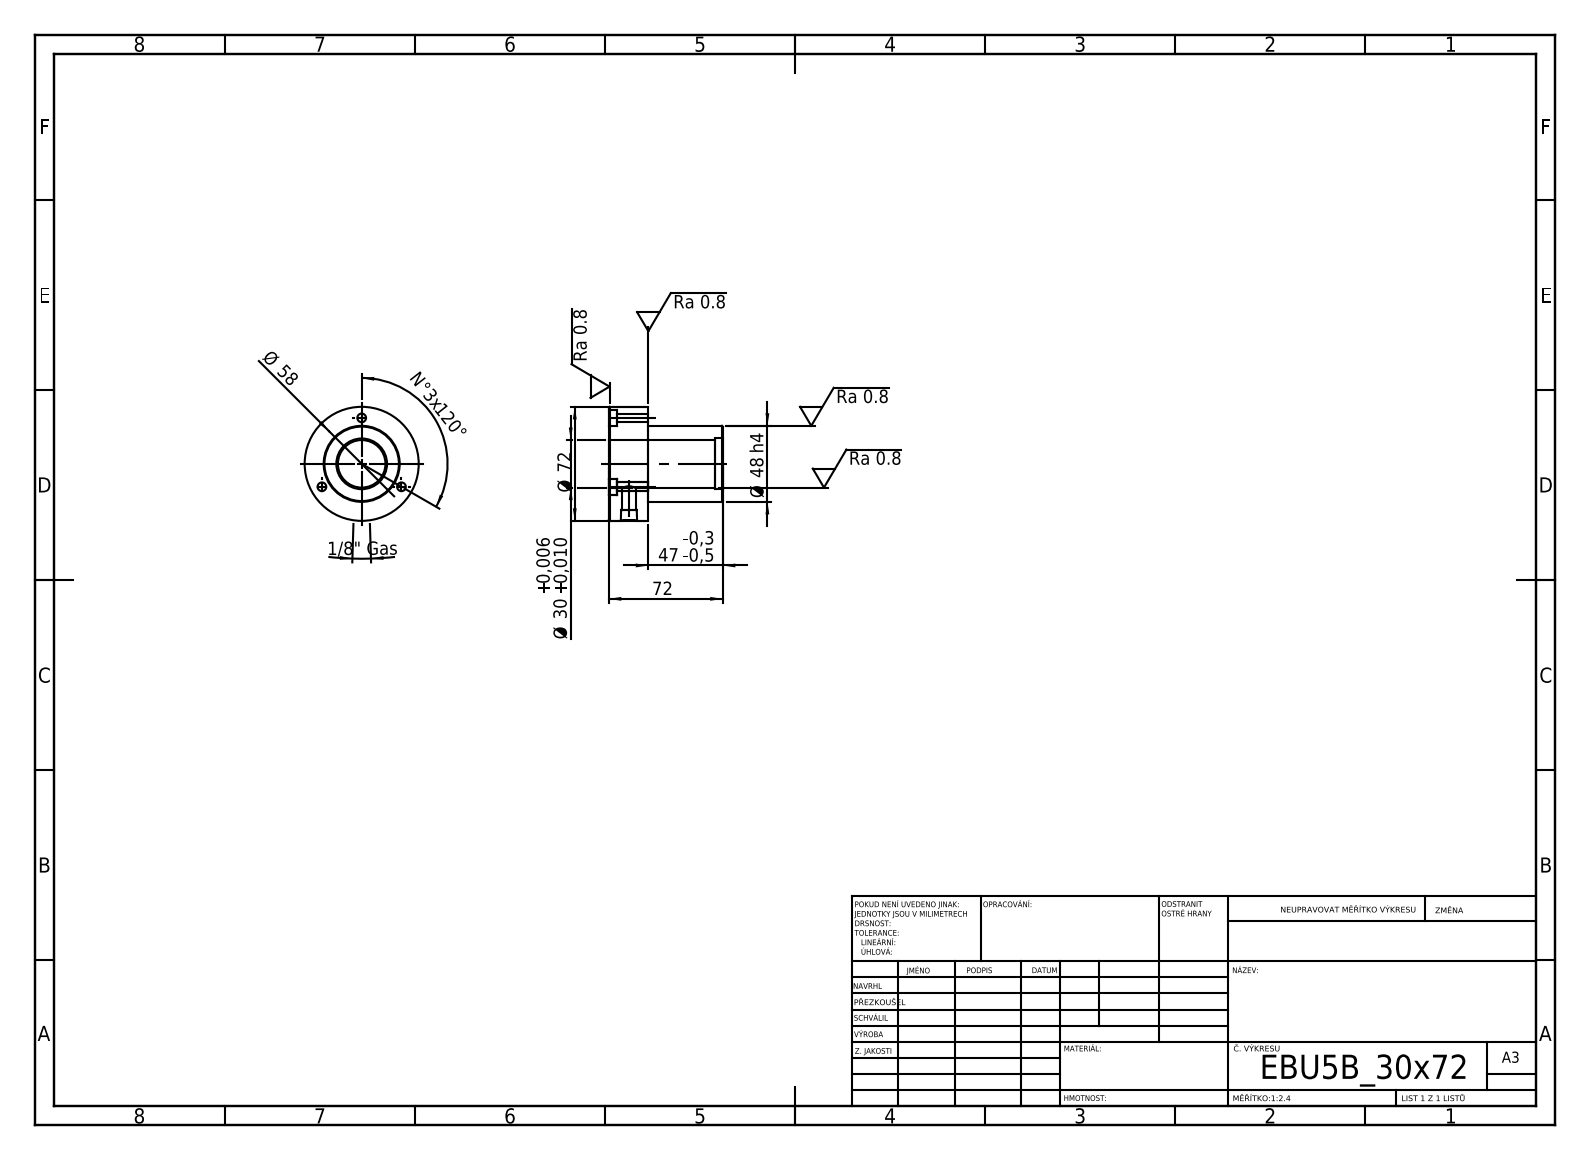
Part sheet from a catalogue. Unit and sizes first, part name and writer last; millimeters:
Units: millimetres
Overall size (bounding box): 72 × 72 × 72
Round holes (diameter × count): ⌀5.5 ×3, ⌀10 ×3, ⌀8.43 ×1, ⌀30 ×1, ⌀32 ×1
Round bosses / shafts (diameter × count): ⌀72 ×1, ⌀48 ×1
Main face-to-face distances: 25, 47, 72, 66.6, 19.6, 5.4, 5, 42, 61.6, 67
Hole centre spacings: 29, 50.23, 50.22
Volume: 131 400 mm³ · Surface area: 28 036 mm²
Bodies: 1 solid, 36 faces (8 planar, 22 cylindrical, 6 other)
STEP written by: SolidWorks 2019 (CONFIG_CONTROL_DESIGN)
